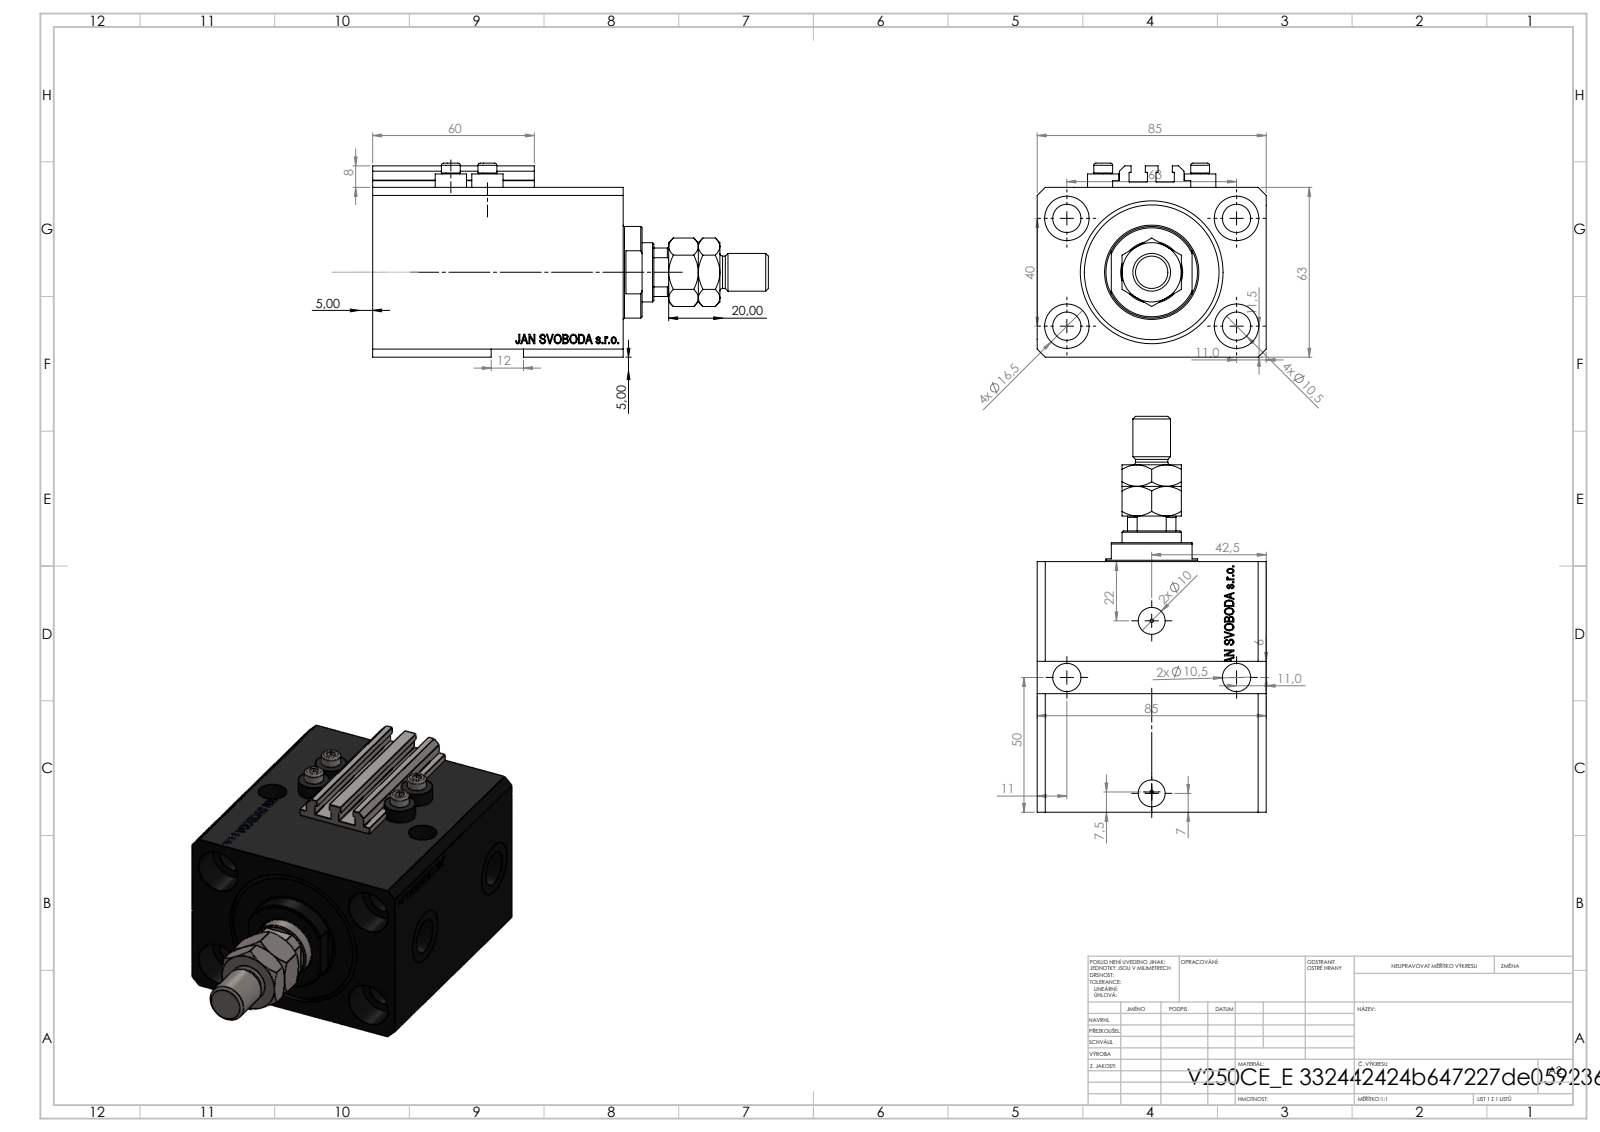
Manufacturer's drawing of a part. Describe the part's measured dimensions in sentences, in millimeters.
The part is named "V250CE_VC_E; V250CE_E_Body; MTA; V250CE_C_VCP (+1 more)". Its 3-D file was written by "SolidWorks 2019 (CONFIG_CONTROL_DESIGN)". It is 9 solids with 1136 faces: 550 planar, 130 cylindrical and 456 other. Overall it measures 147 by 85 by 72 millimeters. Its volume is 447 792 cubic millimeters and its surface area 98 828 square millimeters. Round holes: 6 of diameter 10.5, 4 of diameter 1.25, 4 of diameter 4, 4 of diameter 16.5, 2 of diameter 10, 2 of diameter 13.16, 2 of diameter 20, 1 of diameter 12.5, 1 of diameter 22, 1 of diameter 40, 1 of diameter 53. Round bosses or shafts: 4 of diameter 11.6, 4 of diameter 7, 1 of diameter 34, 1 of diameter 14, 1 of diameter 12. Partial cylindrical surfaces (rounded edges, fillets, slot ends): 10 of radius 0.2, 1 of radius 10.5. The main face-to-face distances are 63, 85, 17, 93, 76, 11.4, 64.6, 81.6, 3, 65. The hole center spacings are 37.31, 63, 13.6, 15.4, 24.96, 28.02, 28.43, 33.62.
